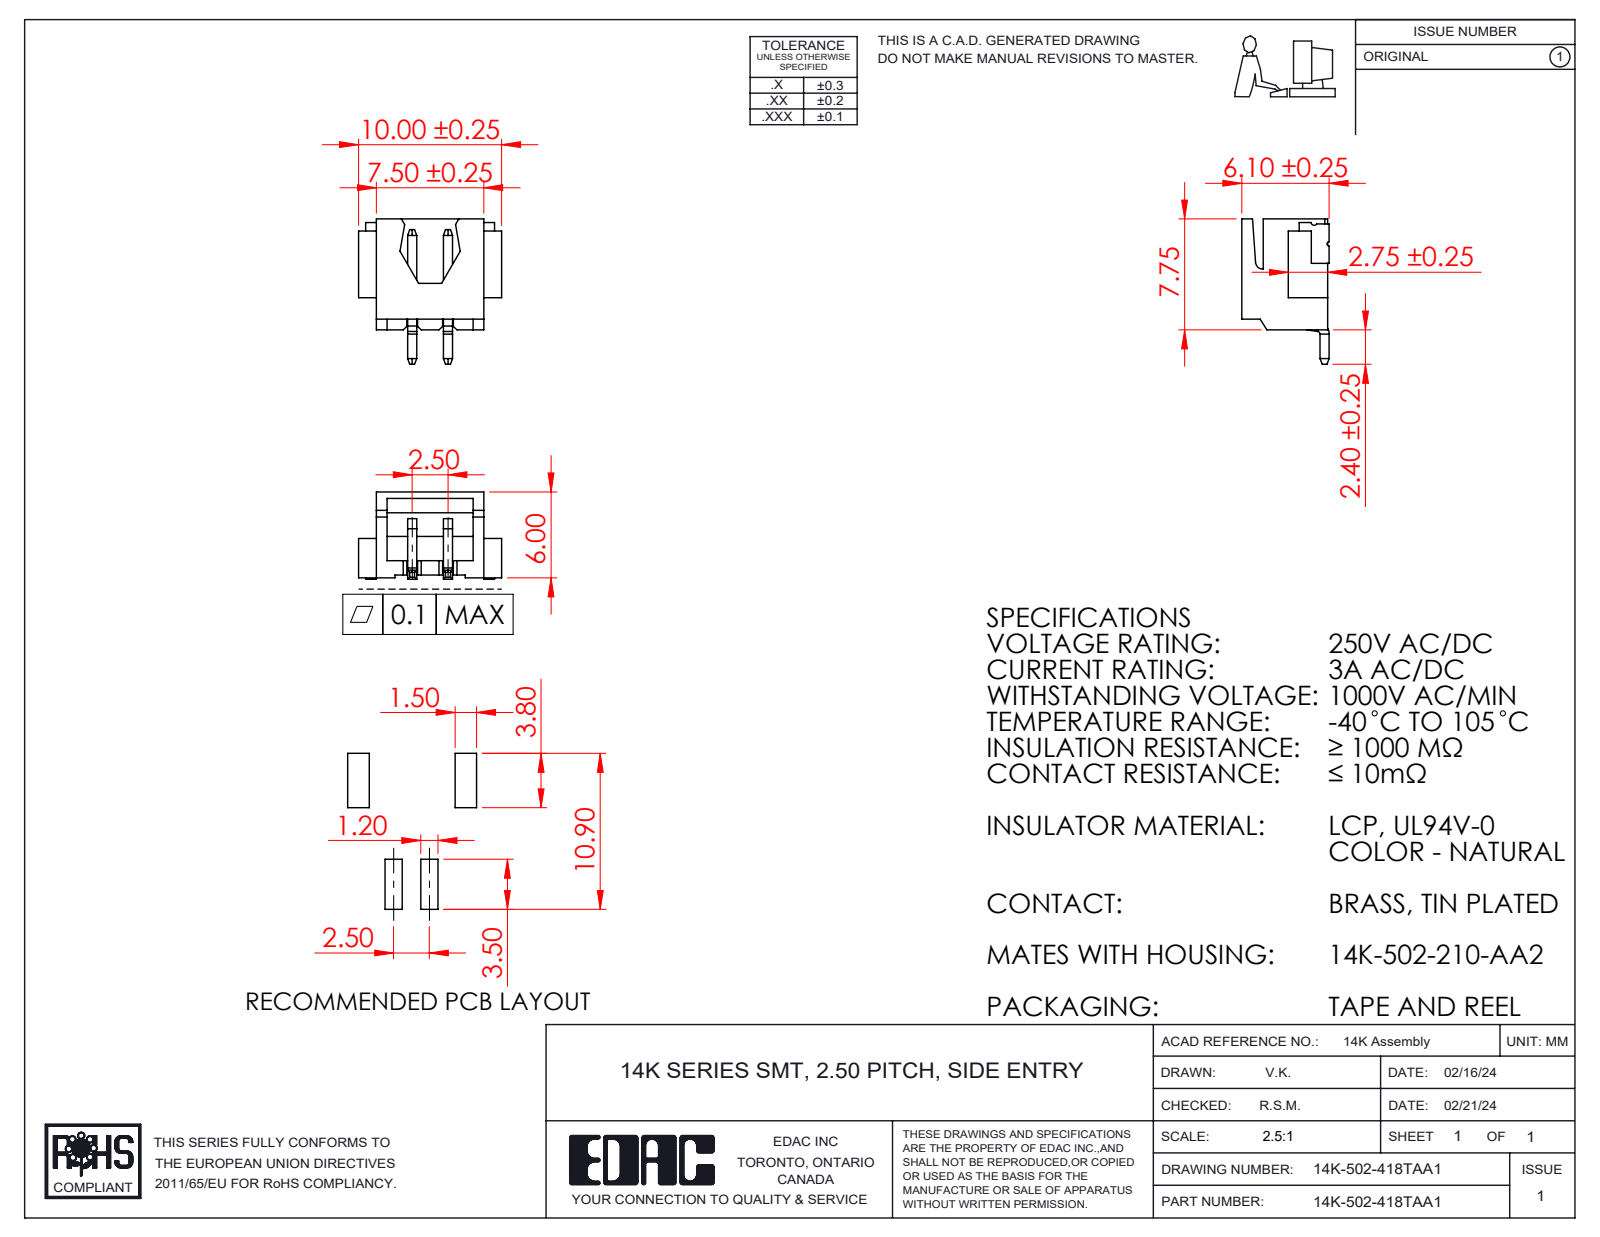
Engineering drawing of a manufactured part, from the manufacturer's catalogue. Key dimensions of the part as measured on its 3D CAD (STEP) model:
Part name (STEP PRODUCT): 14K Series SMT Pin_Side Entry; 14K Series SMT Side Entry Insulator_502; 14K-502-418TAA1
STEP written by: SolidWorks 2023 (CONFIG_CONTROL_DESIGN)
Units: millimetres
Bodies: 3 solids, 185 faces (166 planar, 19 cylindrical, 0 other)
Overall size (bounding box): 10.15 × 10 × 6.1
Volume: 185 mm³ · Surface area: 534 mm²
Partial cylindrical surfaces — rounded edges, fillets, slot ends (radius × count): R0.38 ×4, R0.18 ×2, R0.82 ×2, R0.14 ×1, R0.2 ×1, R0.5 ×1
Main face-to-face distances: 0.75, 6, 6.75, 5.05, 2.5, 7.5, 1.25, 5.8, 0.5, 2
